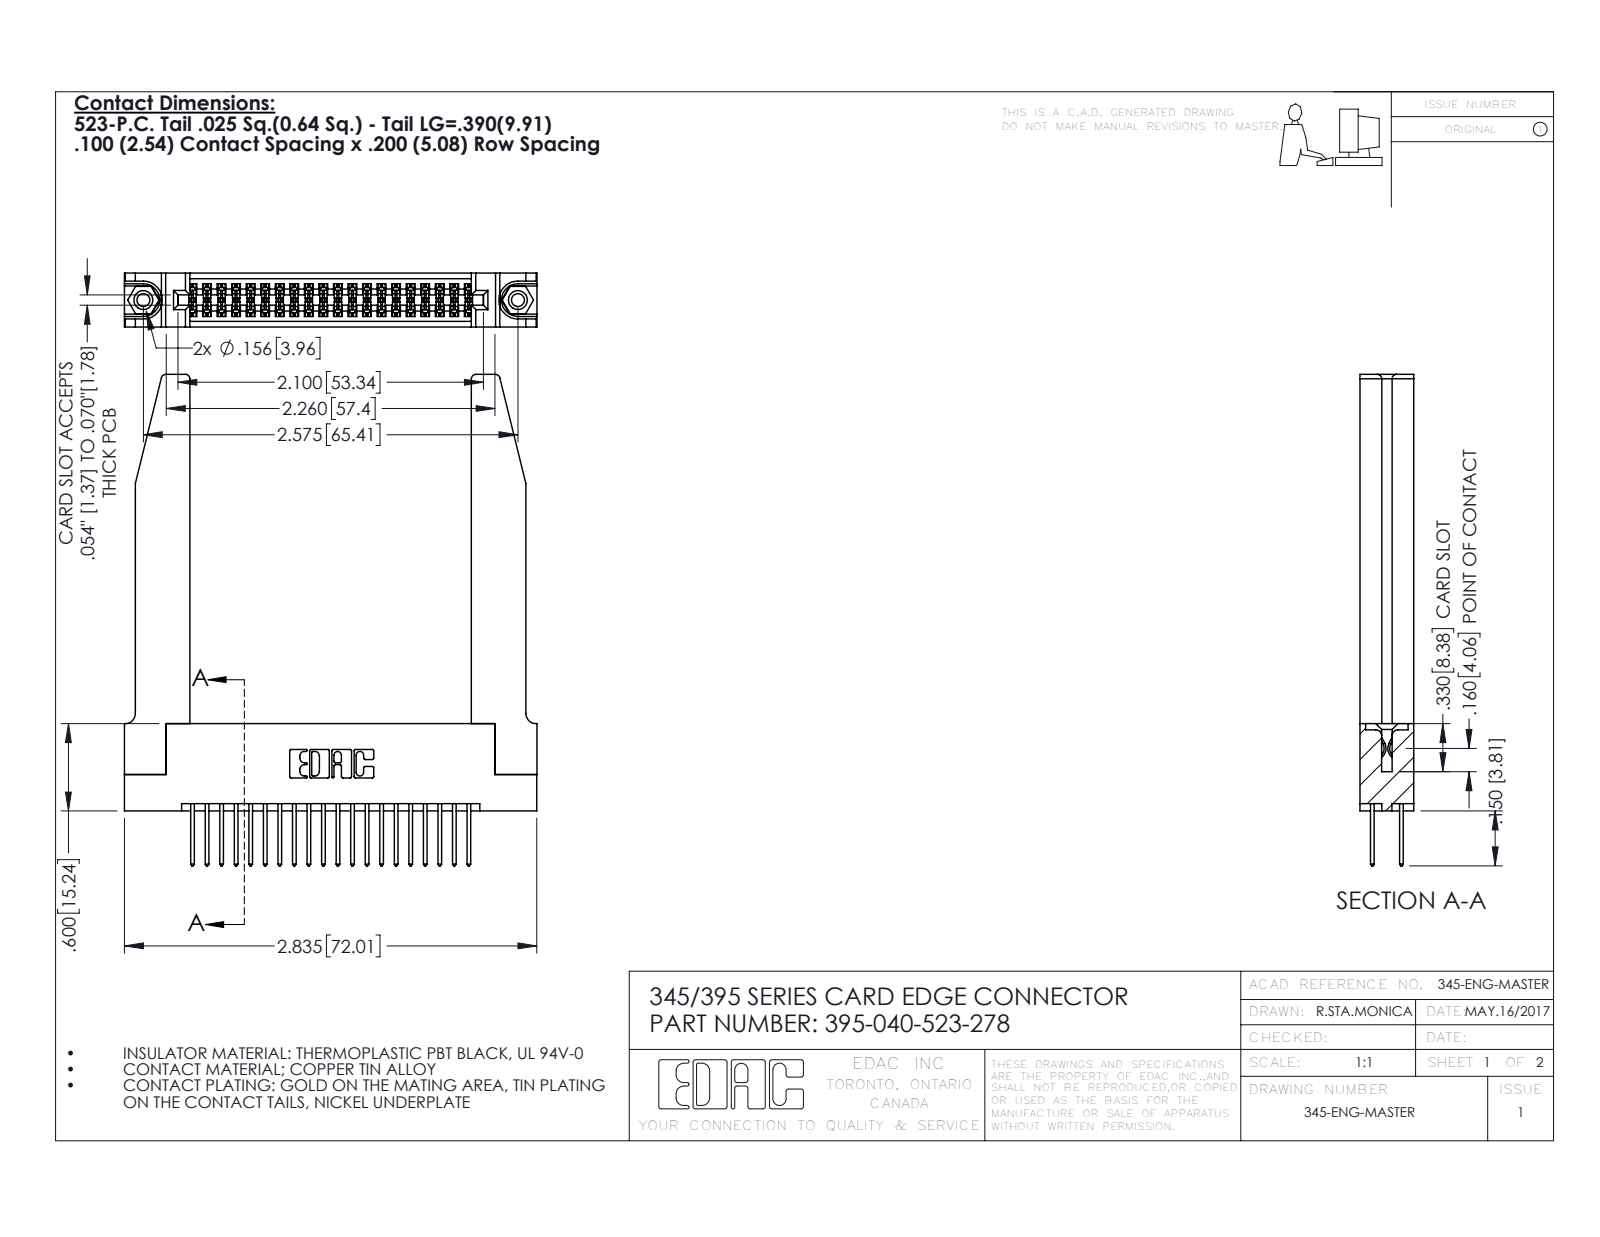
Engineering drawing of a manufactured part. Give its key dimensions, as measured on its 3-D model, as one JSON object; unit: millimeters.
{"part_name": "345 Part_Flush Mounting Lugs - 0.156 Dia-TH; 345-292-001_345-293-123; 345-220-078_345-220-078; 395-040-523-278 (+1 more)", "step_written_by": "SolidWorks 2016 (CONFIG_CONTROL_DESIGN)", "units": "millimeters", "bodies": {"solids": 45, "faces": 2360, "planar": 1542, "cylindrical": 766, "other": 52}, "overall_size": [85.8, 72, 9.4], "volume_mm3": 14700, "surface_area_mm2": 16940, "round_holes": [[2.3, 2], [3.2, 2], [4, 2], [1.6, 1]], "round_bosses_or_shafts": [[3.9, 2]], "partial_cylinders_radius": [[0.2, 60], [0.3, 40], [0.3, 22], [0.8, 8], [0.2, 6], [0.8, 6], [0.7, 3], [0.4, 2]], "face_to_face_distances": [9.4, 1.8, 7.6, 5.1, 2.5, 6.9, 0.6, 5.7, 3.8, 3.8], "hole_center_spacings": [6.9, 59.5, 65.4]}
